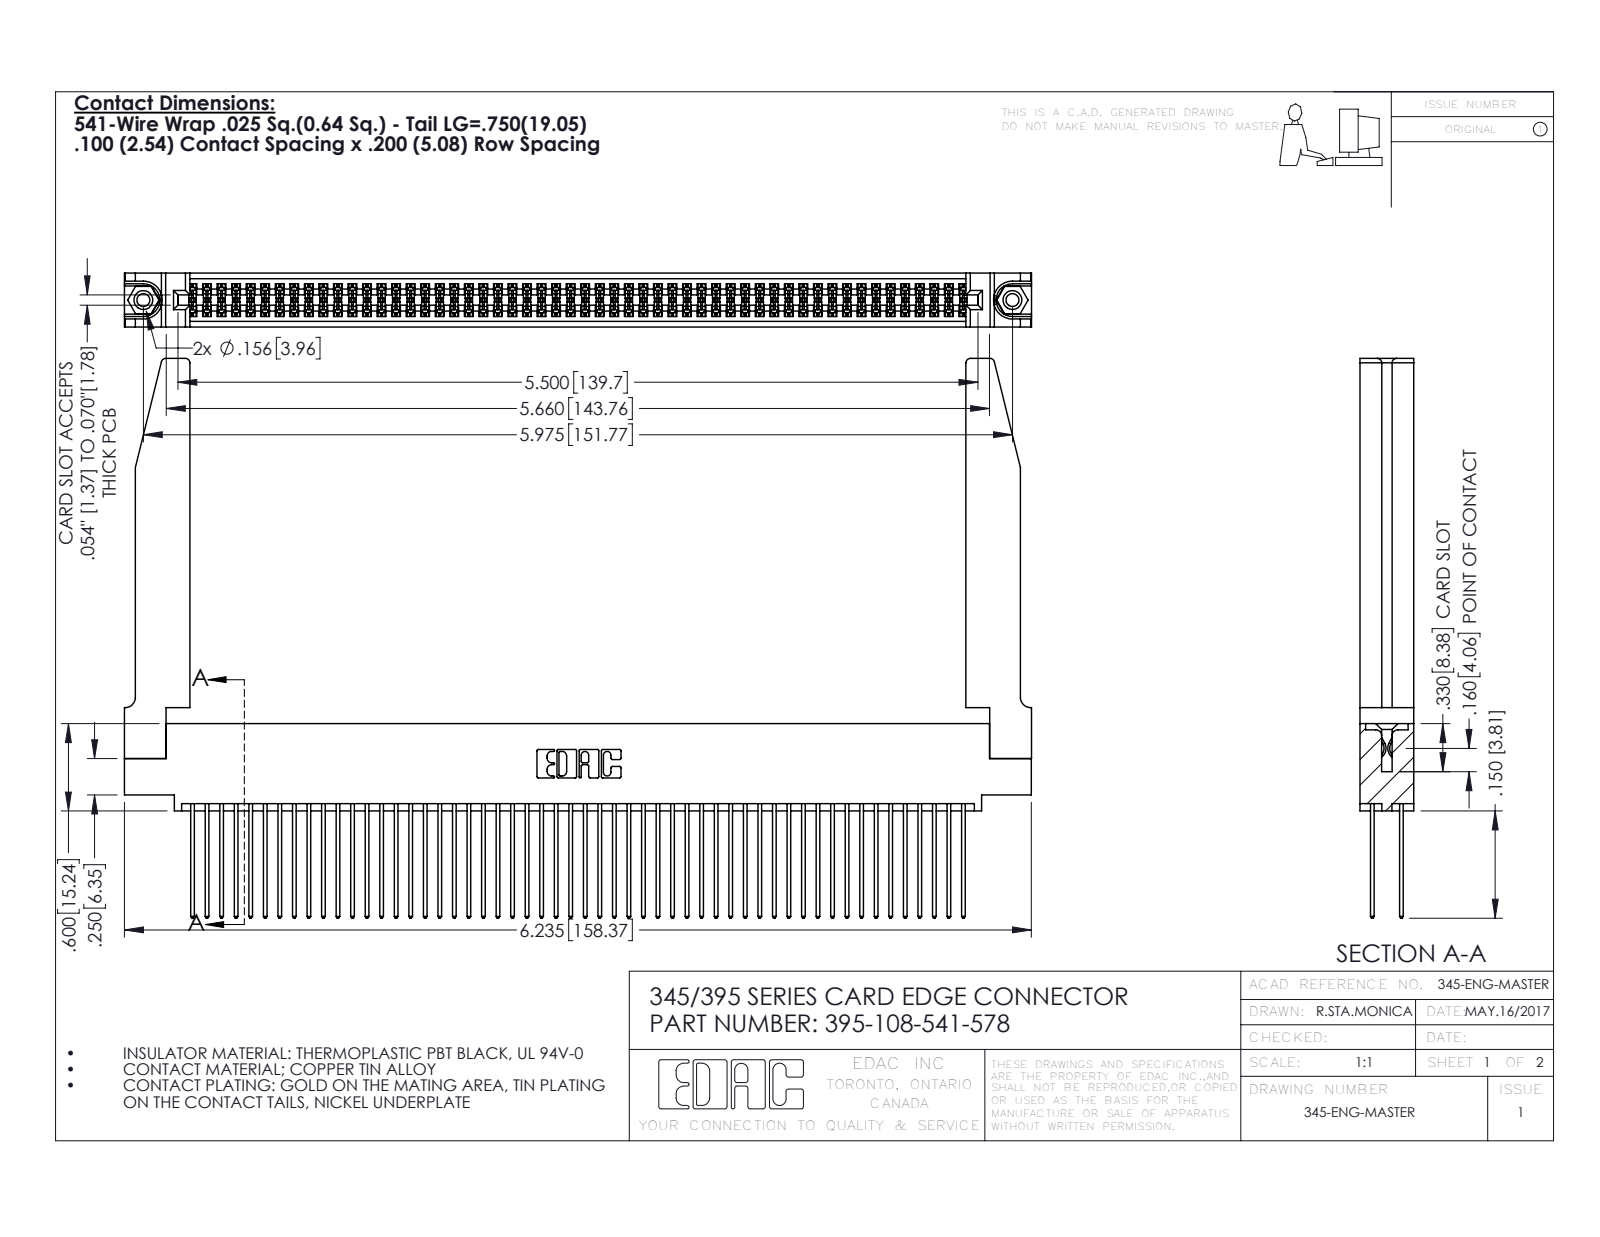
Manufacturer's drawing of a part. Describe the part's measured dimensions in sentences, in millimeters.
The part is named "345-220-078_345-220-078; 345-292-001_345-293-141; 395-108-541-578; 345 Part_0.110 Offset - 0.156 Dia-TH (+1 more)". Its 3-D file was written by "SolidWorks 2016 (CONFIG_CONTROL_DESIGN)". It is 113 solids with 5764 faces: 3790 planar, 1922 cylindrical and 52 other. Overall it measures 158.4 by 97.7 by 9.4 millimeters. Its volume is 23 810 cubic millimeters and its surface area 33 790 square millimeters. Round holes: 2 of diameter 2.3, 2 of diameter 3.2, 2 of diameter 4, 1 of diameter 1.6. Round bosses or shafts: 2 of diameter 3.9. Partial cylindrical surfaces (rounded edges, fillets, slot ends): 162 of radius 0.2, 108 of radius 0.3, 22 of radius 0.3, 8 of radius 0.8, 6 of radius 0.2, 6 of radius 0.8, 3 of radius 0.7, 2 of radius 0.4. The main face-to-face distances are 1.8, 7.6, 9.4, 5.1, 2.5, 6.9, 0.6, 5.7, 4.4, 3.8. The hole center spacings are 6.9, 145.8, 151.8.
